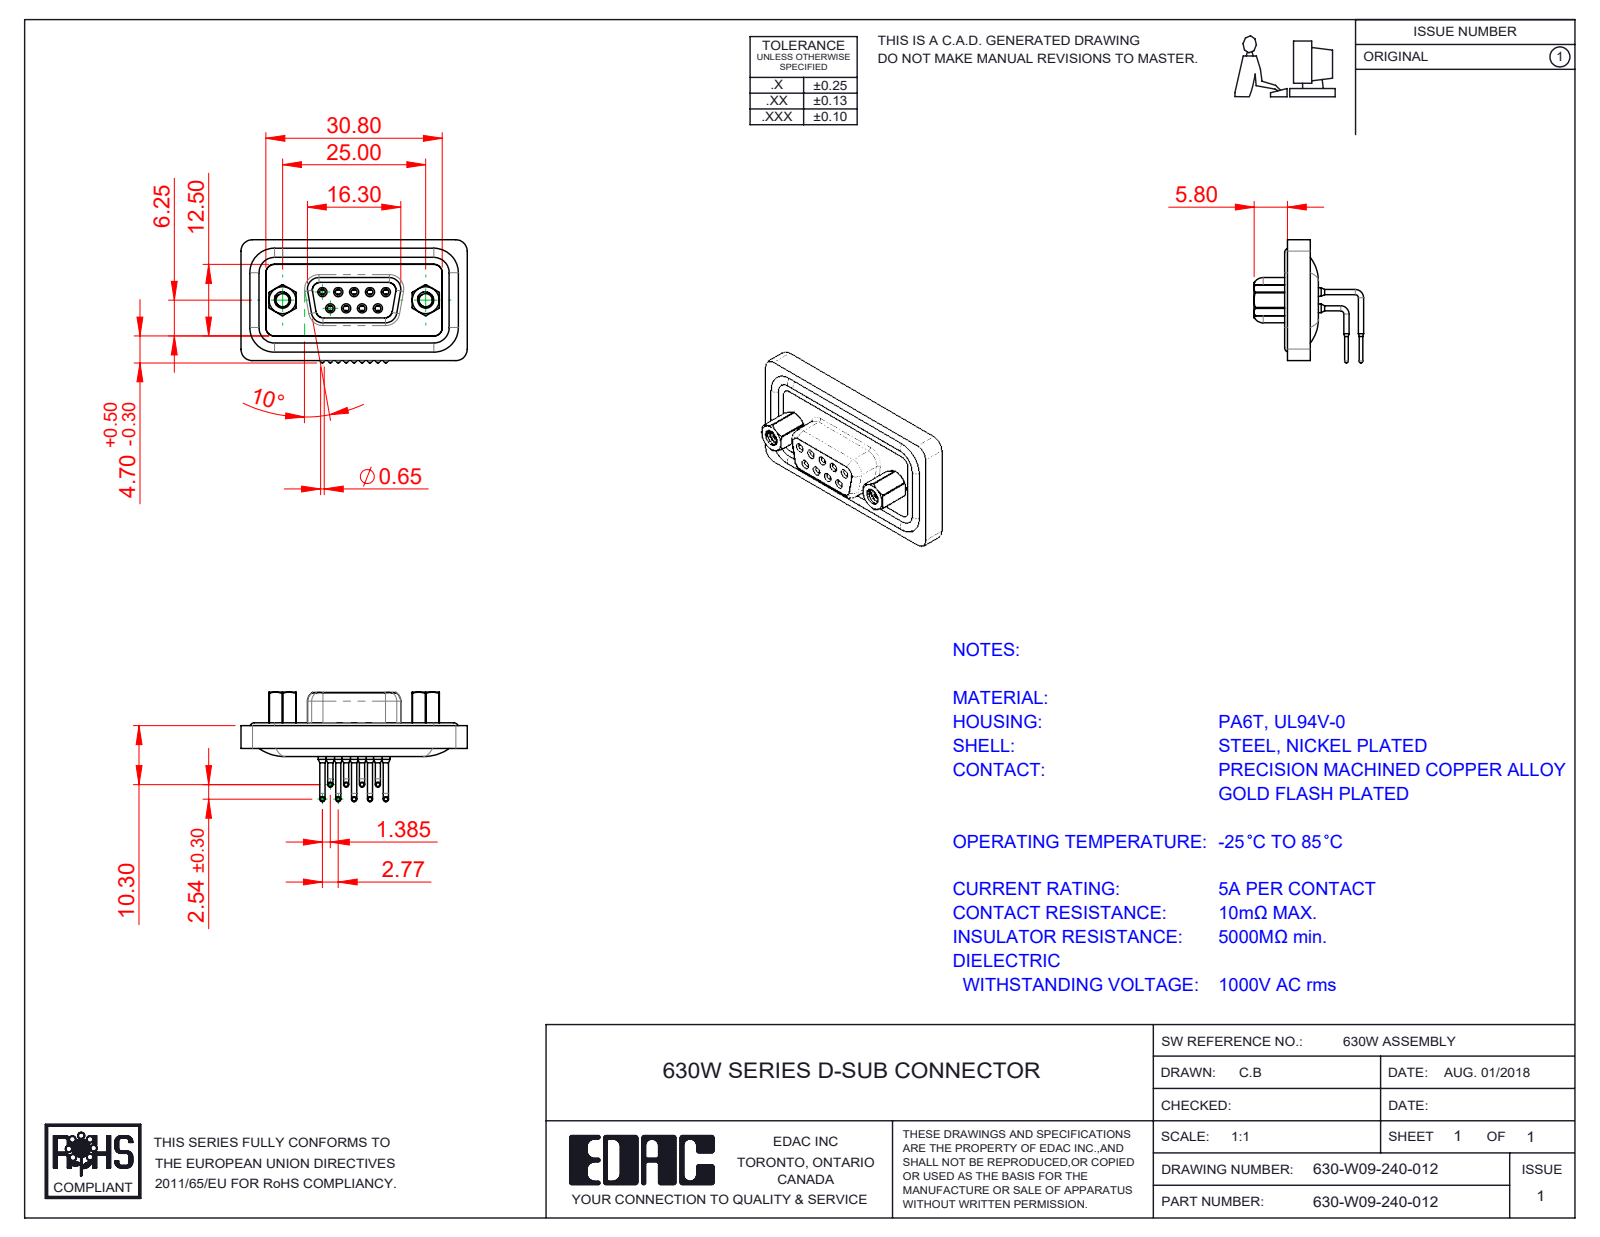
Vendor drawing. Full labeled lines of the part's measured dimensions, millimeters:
Part name (STEP PRODUCT): 630W Shell_09 Contacts; 630W 4-40 Hex Standoff; 630W Housing_09 Contacts; 630W Contact Row 2 (+4 more)
STEP written by: SolidWorks 2016 (CONFIG_CONTROL_DESIGN)
Units: millimetres
Bodies: 17 solids, 910 faces (236 planar, 437 cylindrical, 237 other)
Overall size (bounding box): 39.51 × 21.5 × 19.14
Volume: 4 411 mm³ · Surface area: 7 420 mm²
Round holes (diameter × count): ⌀1 ×9, ⌀1.1 ×9, ⌀1.5 ×9, ⌀1.7 ×9, ⌀1.8 ×9, ⌀2 ×9, ⌀2.26 ×2, ⌀2.29 ×2, ⌀4 ×2, ⌀4.8 ×2, ⌀5 ×2
Round bosses / shafts (diameter × count): ⌀0.9 ×18, ⌀1.6 ×13, ⌀0.65 ×9, ⌀1.5 ×4, ⌀4.9 ×2, ⌀2.79 ×2, ⌀5 ×1
Partial cylindrical surfaces — rounded edges, fillets, slot ends (radius × count): R1.5 ×14, R2 ×14, R1.35 ×8, R2.7 ×6, R0.5 ×4, R0.9 ×4, R1.6 ×4, R1.75 ×4
Main face-to-face distances: 0.4, 1.6, 1.8, 1.1, 2.9, 2.5, 0.5, 3.6, 4, 0.7
Hole centre spacings: 3.16, 2.77, 5.54, 5.03, 5.04, 7.48, 7.49, 8.31
